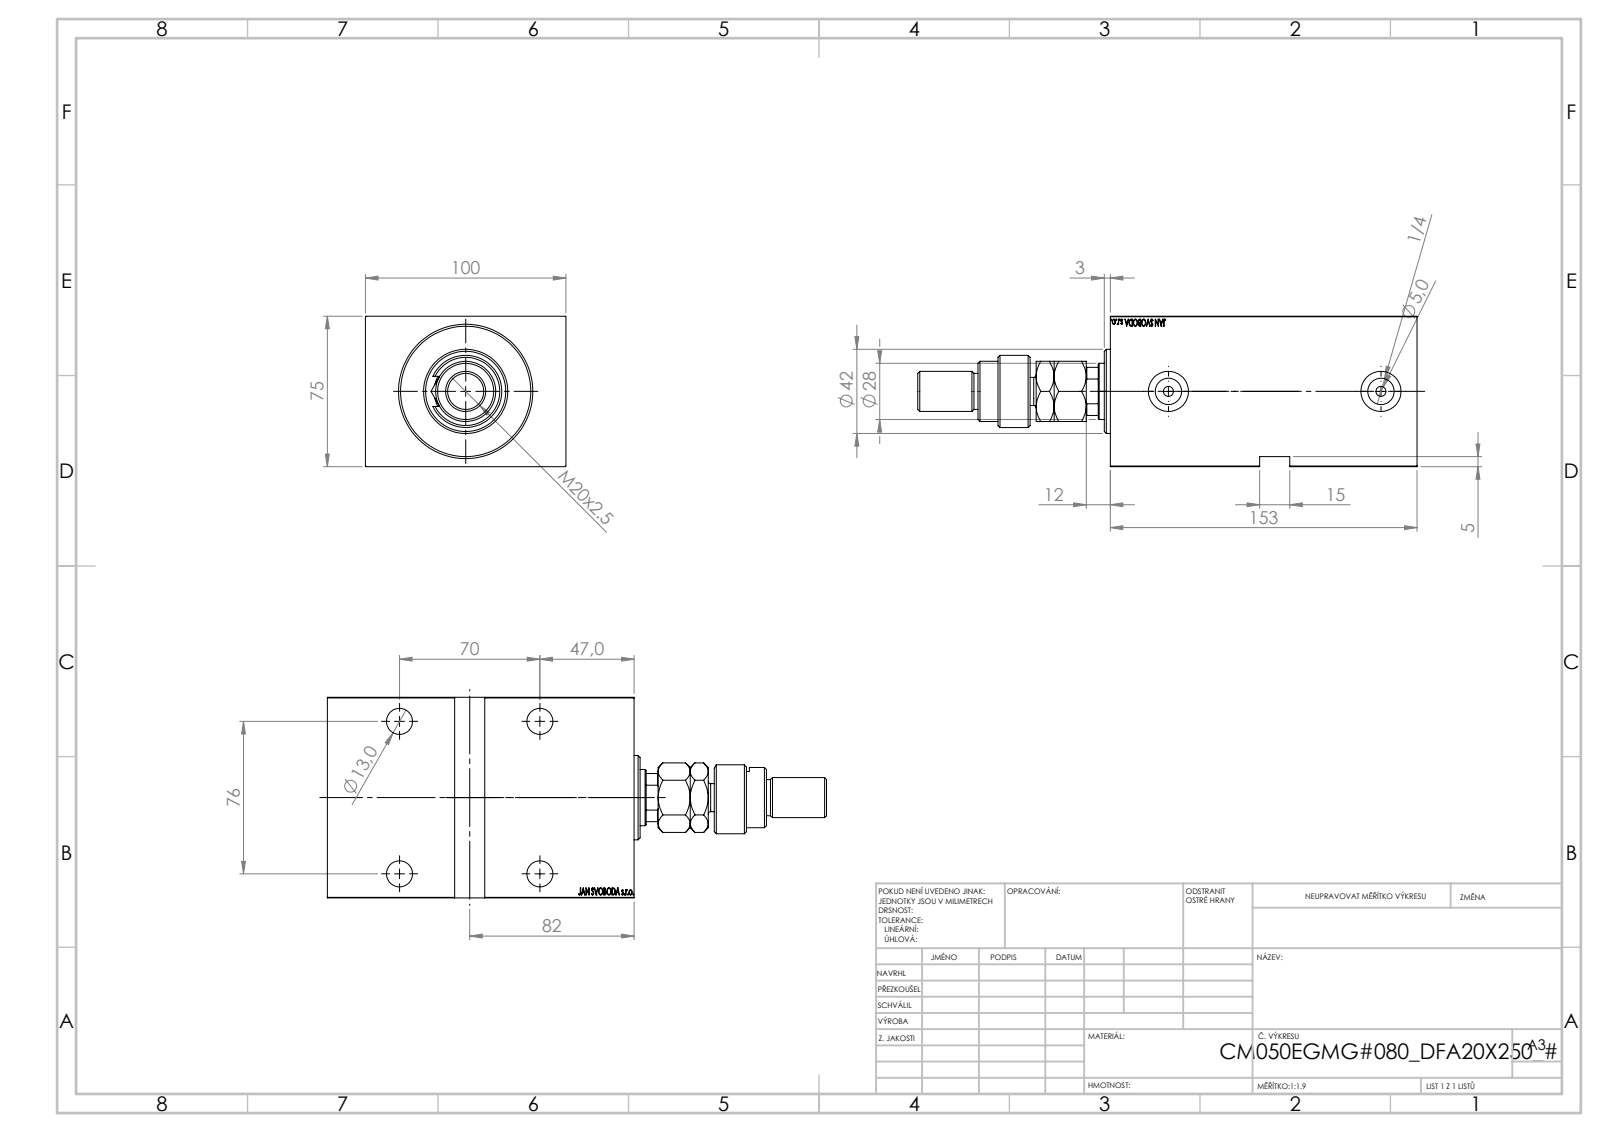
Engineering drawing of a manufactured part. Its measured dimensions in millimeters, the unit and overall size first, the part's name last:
Units: millimetres
Overall size (bounding box): 249 × 100 × 75
Round holes (diameter × count): ⌀13 ×4, ⌀19 ×4, ⌀5 ×2, ⌀13.16 ×2, ⌀20 ×2, ⌀18.5 ×1, ⌀28 ×1, ⌀31.5 ×1, ⌀50 ×1, ⌀52 ×1, ⌀65 ×1
Round bosses / shafts (diameter × count): ⌀42 ×1, ⌀36 ×1, ⌀30 ×1, ⌀22 ×1, ⌀20 ×1, ⌀18 ×1, ⌀14 ×1
Partial cylindrical surfaces — rounded edges, fillets, slot ends (radius × count): R7.5 ×1, R12 ×1, R13.5 ×1
Main face-to-face distances: 75, 100, 153, 14, 139, 5, 148, 134, 30, 136.4
Hole centre spacings: 70, 76, 103.32, 106
Volume: 1 006 000 mm³ · Surface area: 150 031 mm²
Bodies: 5 solids, 946 faces (441 planar, 67 cylindrical, 438 other)
Part name (STEP PRODUCT): MFA; V450CM_E_Body; V450CM_E_VCP; V450CM_VC_B (+1 more)
STEP written by: SolidWorks 2019 (CONFIG_CONTROL_DESIGN)
